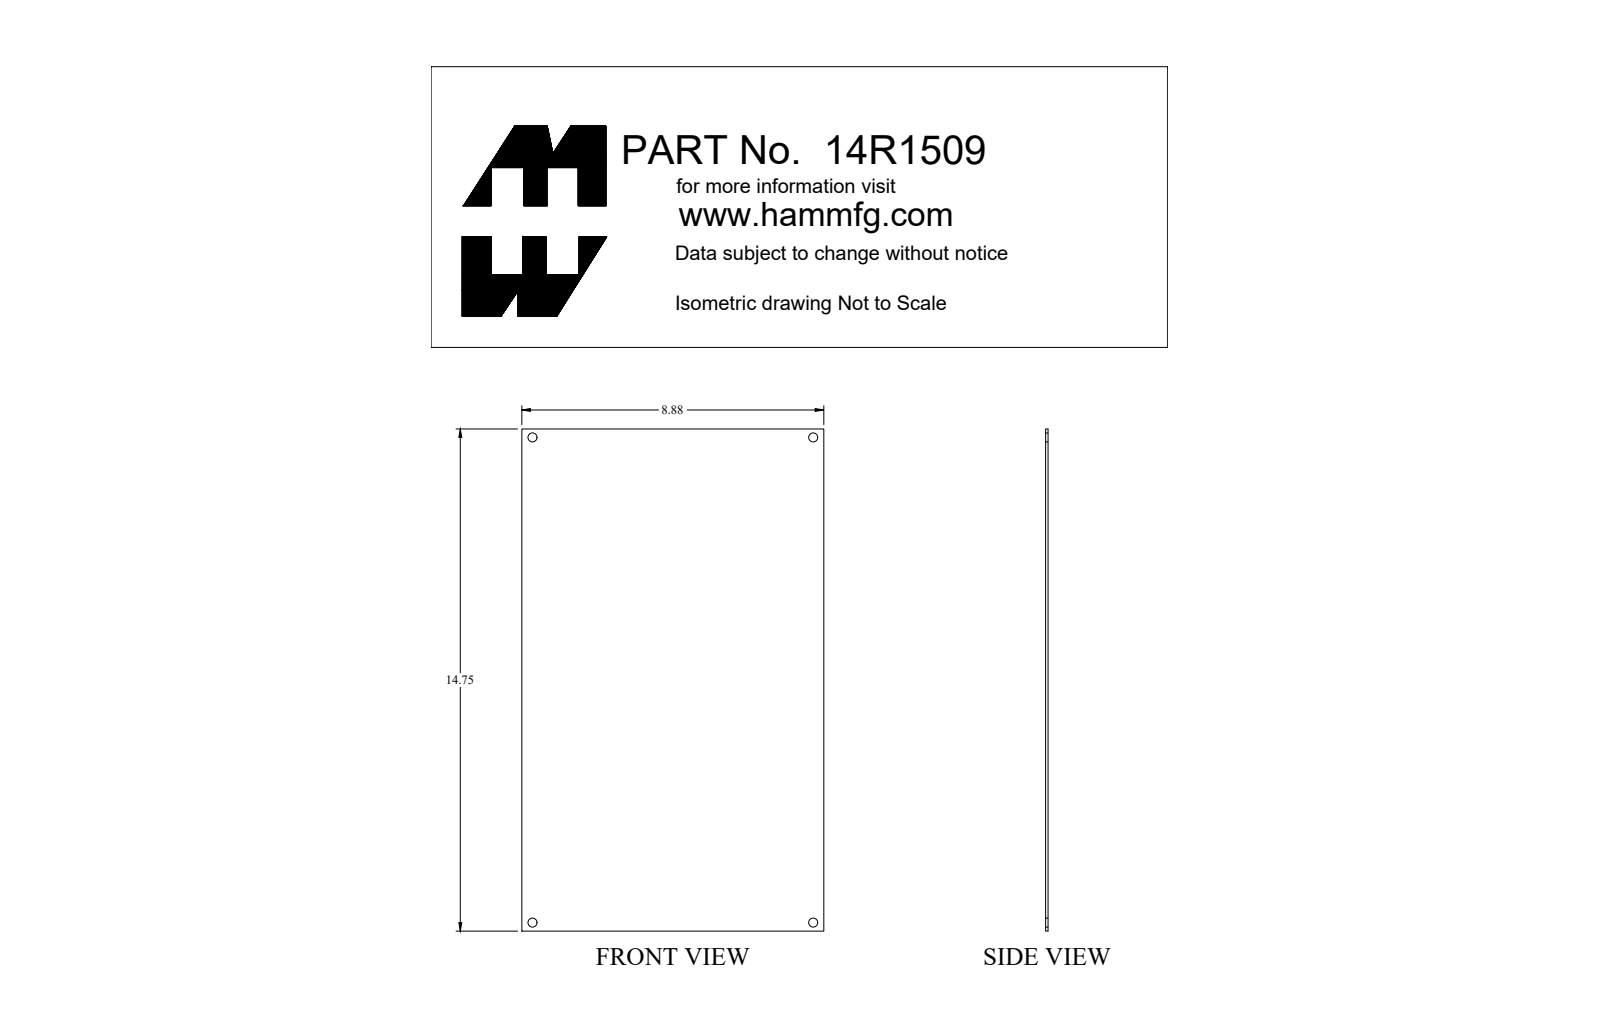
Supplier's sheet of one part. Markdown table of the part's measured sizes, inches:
| quantity | value |
| --- | --- |
| part name | 14R1509 |
| STEP written by | SolidWorks 2018 (AUTOMOTIVE_DESIGN) |
| units | inches |
| bodies | 1 solid, 10 faces (6 planar, 4 cylindrical, 0 other) |
| overall size | 14.75 × 8.875 × 0.072 |
| volume | 9.409 in³ |
| surface area | 265 in² |
| round holes (diameter × count) | 0.265 × 4 |
| main face-to-face distances | 0.072, 8.875, 14.75 |
| hole center spacings | 8.25, 14.25, 16.465 |
